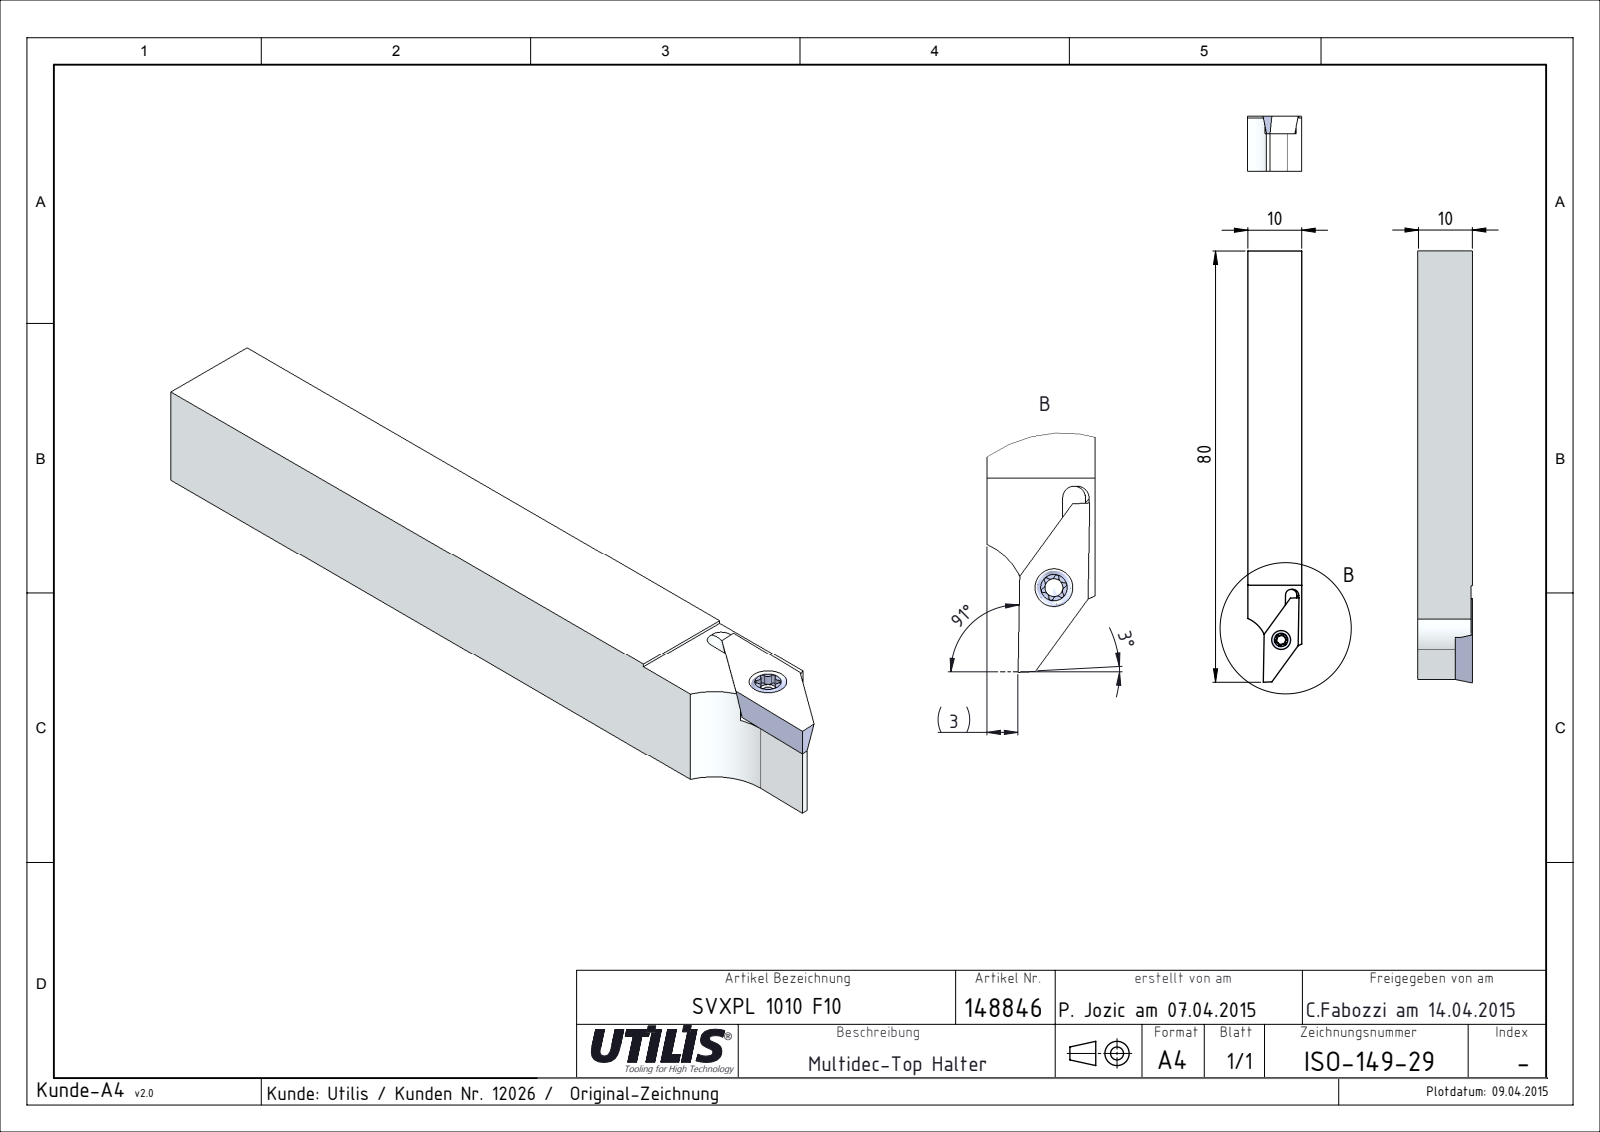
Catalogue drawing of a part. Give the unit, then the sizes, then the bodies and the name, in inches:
Units: inches
Overall size (bounding box): 3.15 × 0.394 × 0.394
Round holes (diameter × count): ⌀0.081 ×1, ⌀0.118 ×1
Round bosses / shafts (diameter × count): ⌀0.136 ×1, ⌀0.098 ×1
Partial cylindrical surfaces — rounded edges, fillets, slot ends (radius × count): R0.008 ×6, R0.018 ×6, R0.236 ×2, R0.041 ×1
Main face-to-face distances: 0.394, 0.269, 0.125, 0.382, 0.113, 0.21, 0.083, 0.127, 0.209, 2.441
Volume: 0.448 in³ · Surface area: 5.509 in²
Bodies: 3 solids, 71 faces (27 planar, 27 cylindrical, 17 other)
Part name (STEP PRODUCT): VPGT 10 L_01; ISO-149-Kunde_29; MSP-7_M2,5X6-TX8 CERATIZIT Schraube; ISO-149-29
STEP written by: SolidWorks 2015 (CONFIG_CONTROL_DESIGN)
